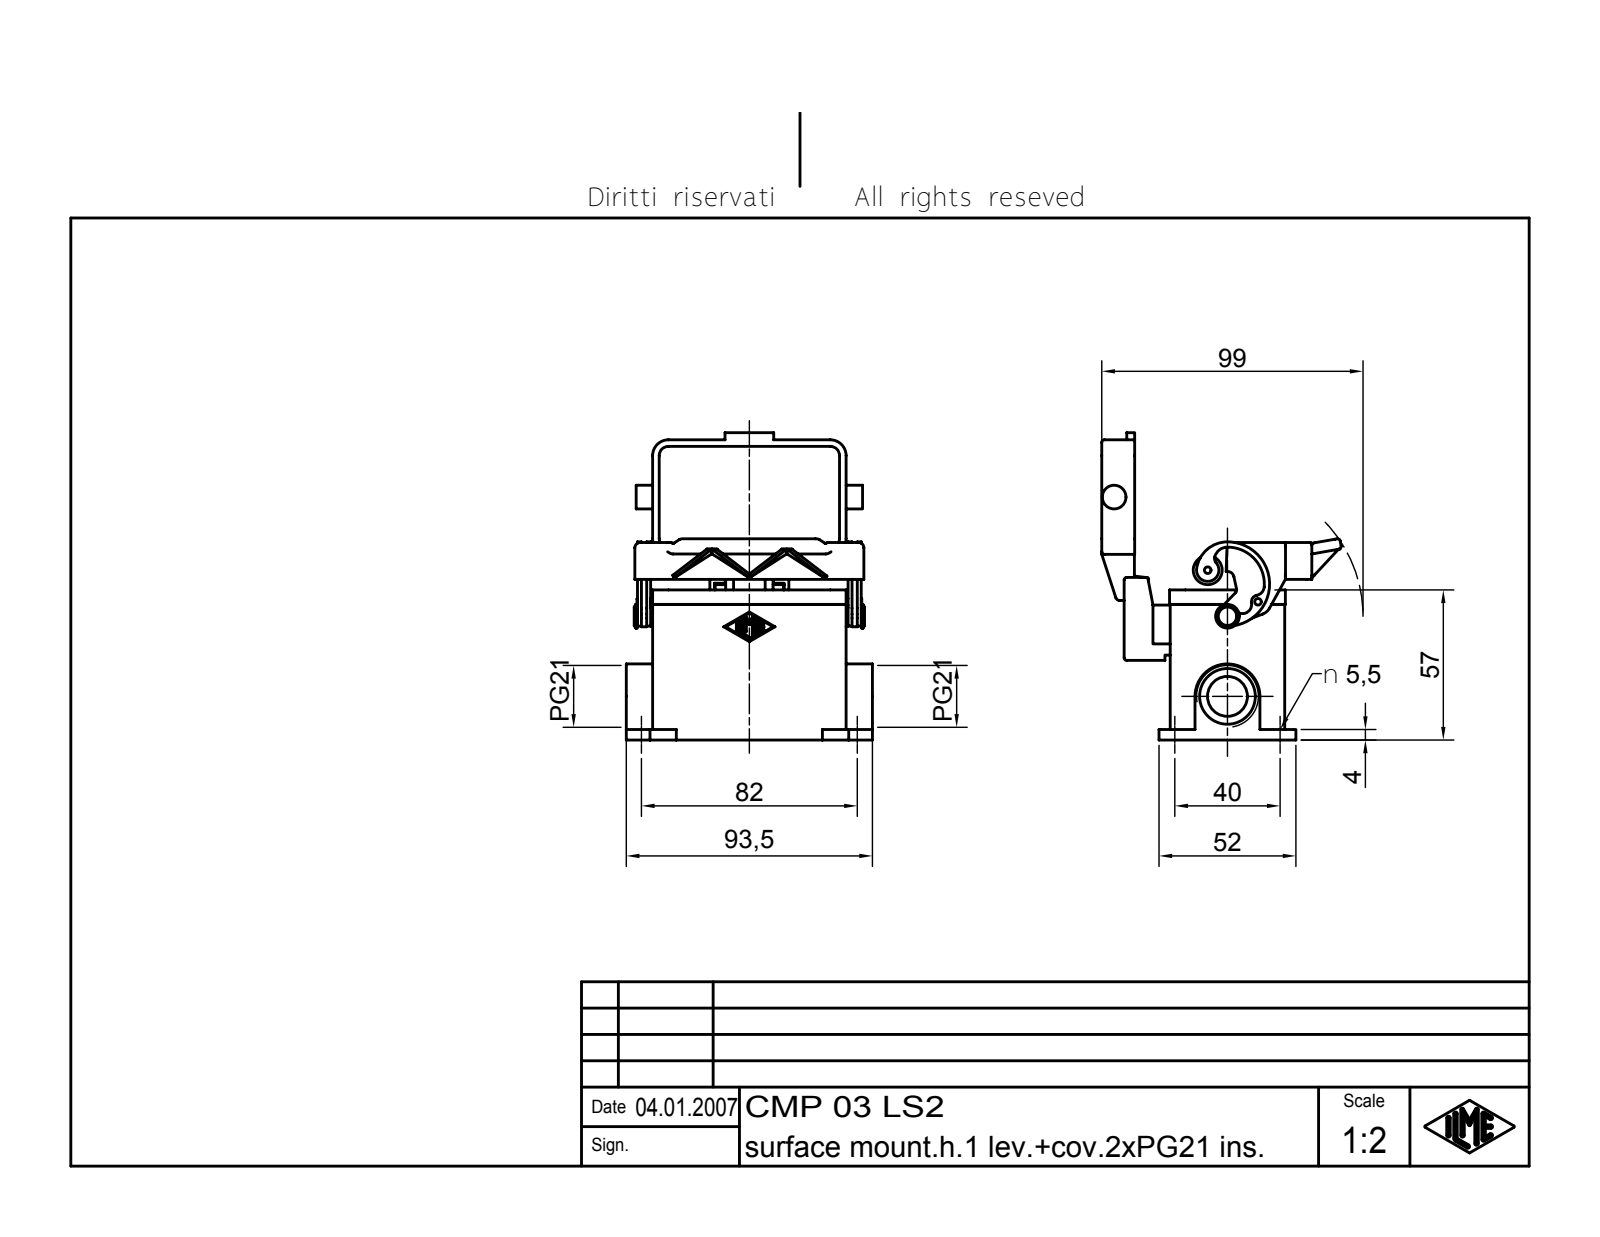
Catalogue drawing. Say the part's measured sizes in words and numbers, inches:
The part is named "CMP 03 LS2". Its 3-D file was written by "Autodesk Inventor 7 (AUTOMOTIVE_DESIGN)". It is 6 solids with 591 faces: 251 planar, 180 cylindrical and 160 other. Overall it measures 4.594 by 3.681 by 3.581 inches. Its volume is 6.881 cubic inches and its surface area 98.66 square inches. Round holes: 4 of diameter 0.217, 1 of diameter 0.079, 1 of diameter 0.157, 1 of diameter 0.597, 1 of diameter 0.833. Round bosses or shafts: 2 of diameter 0.354, 2 of diameter 0.197, 1 of diameter 0.433, 1 of diameter 0.276, 1 of diameter 0.157, 1 of diameter 0.118, 1 of diameter 0.098. Partial cylindrical surfaces (rounded edges, fillets, slot ends): 18 of radius 0.039, 14 of radius 0.015, 12 of radius 0.079, 12 of radius 0.236, 6 of radius 0.059, 6 of radius 0.138, 4 of radius 0.118, 3 of radius 0.02. The main face-to-face distances are 0.118, 0.157, 1.594, 1.024, 1.713, 2.618, 2.736, 2.598, 0.138, 1.004. The hole center spacings are 1.575, 3.228, 3.592, 1.486.
